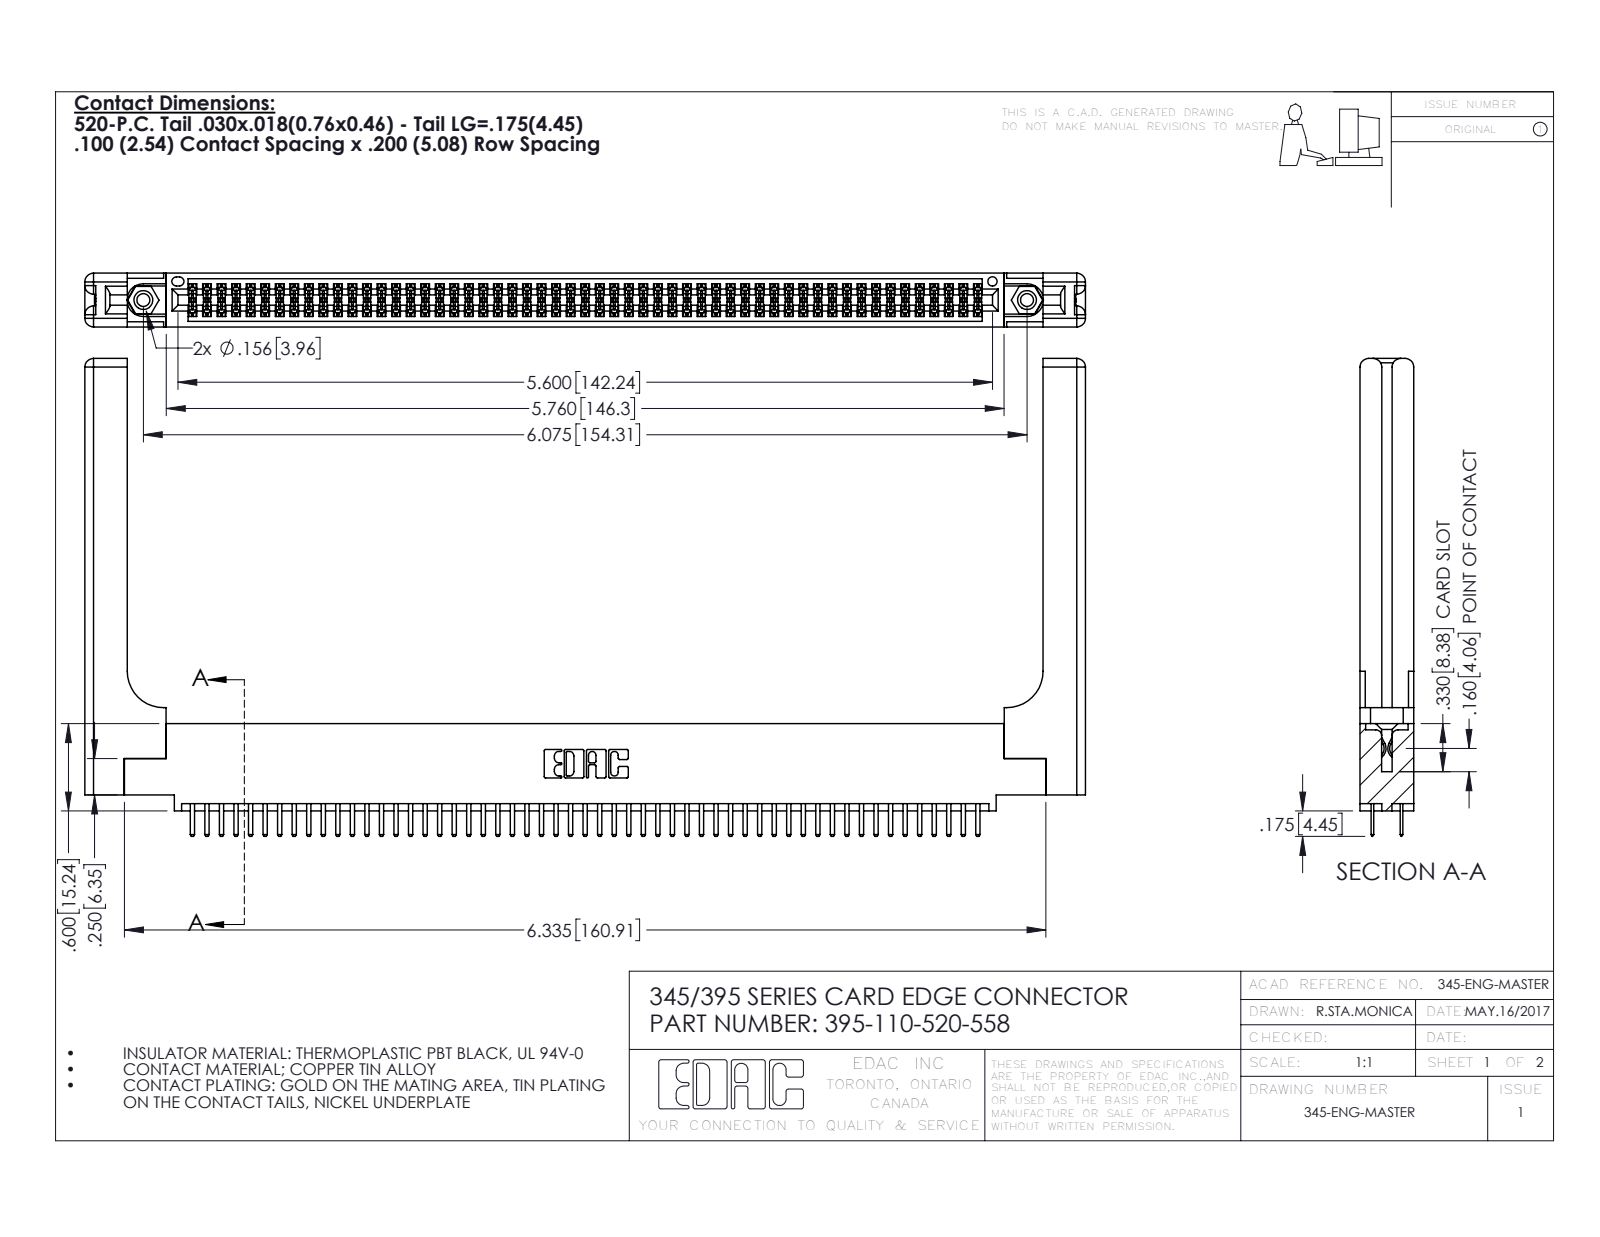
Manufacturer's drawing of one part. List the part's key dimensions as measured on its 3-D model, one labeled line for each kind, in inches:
Part name (STEP PRODUCT): 345 Part_0.110 Offset - 0.156 Dia-TH; 345-250-001_345-250-001-102; 345-292-001_345-293-120; 395-110-520-558 (+1 more)
STEP written by: SolidWorks 2016 (CONFIG_CONTROL_DESIGN)
Units: inches
Bodies: 115 solids, 6326 faces (4082 planar, 2184 cylindrical, 60 other)
Overall size (bounding box): 6.879 × 3.285 × 0.37
Volume: 1.553 in³ · Surface area: 47.1 in²
Round holes (diameter × count): ⌀0.089 ×2, ⌀0.125 ×2, ⌀0.156 ×2, ⌀0.064 ×1
Round bosses / shafts (diameter × count): ⌀0.155 ×2
Partial cylindrical surfaces — rounded edges, fillets, slot ends (radius × count): R0.006 ×165, R0.01 ×114, R0.01 ×22, R0.06 ×16, R0.007 ×6, R0.031 ×6, R0.026 ×3, R0.014 ×2
Main face-to-face distances: 0.072, 0.298, 0.37, 0.2, 0.098, 0.272, 0.025, 0.225, 0.022, 0.148
Hole centre spacings: 0.27, 5.839, 6.075
